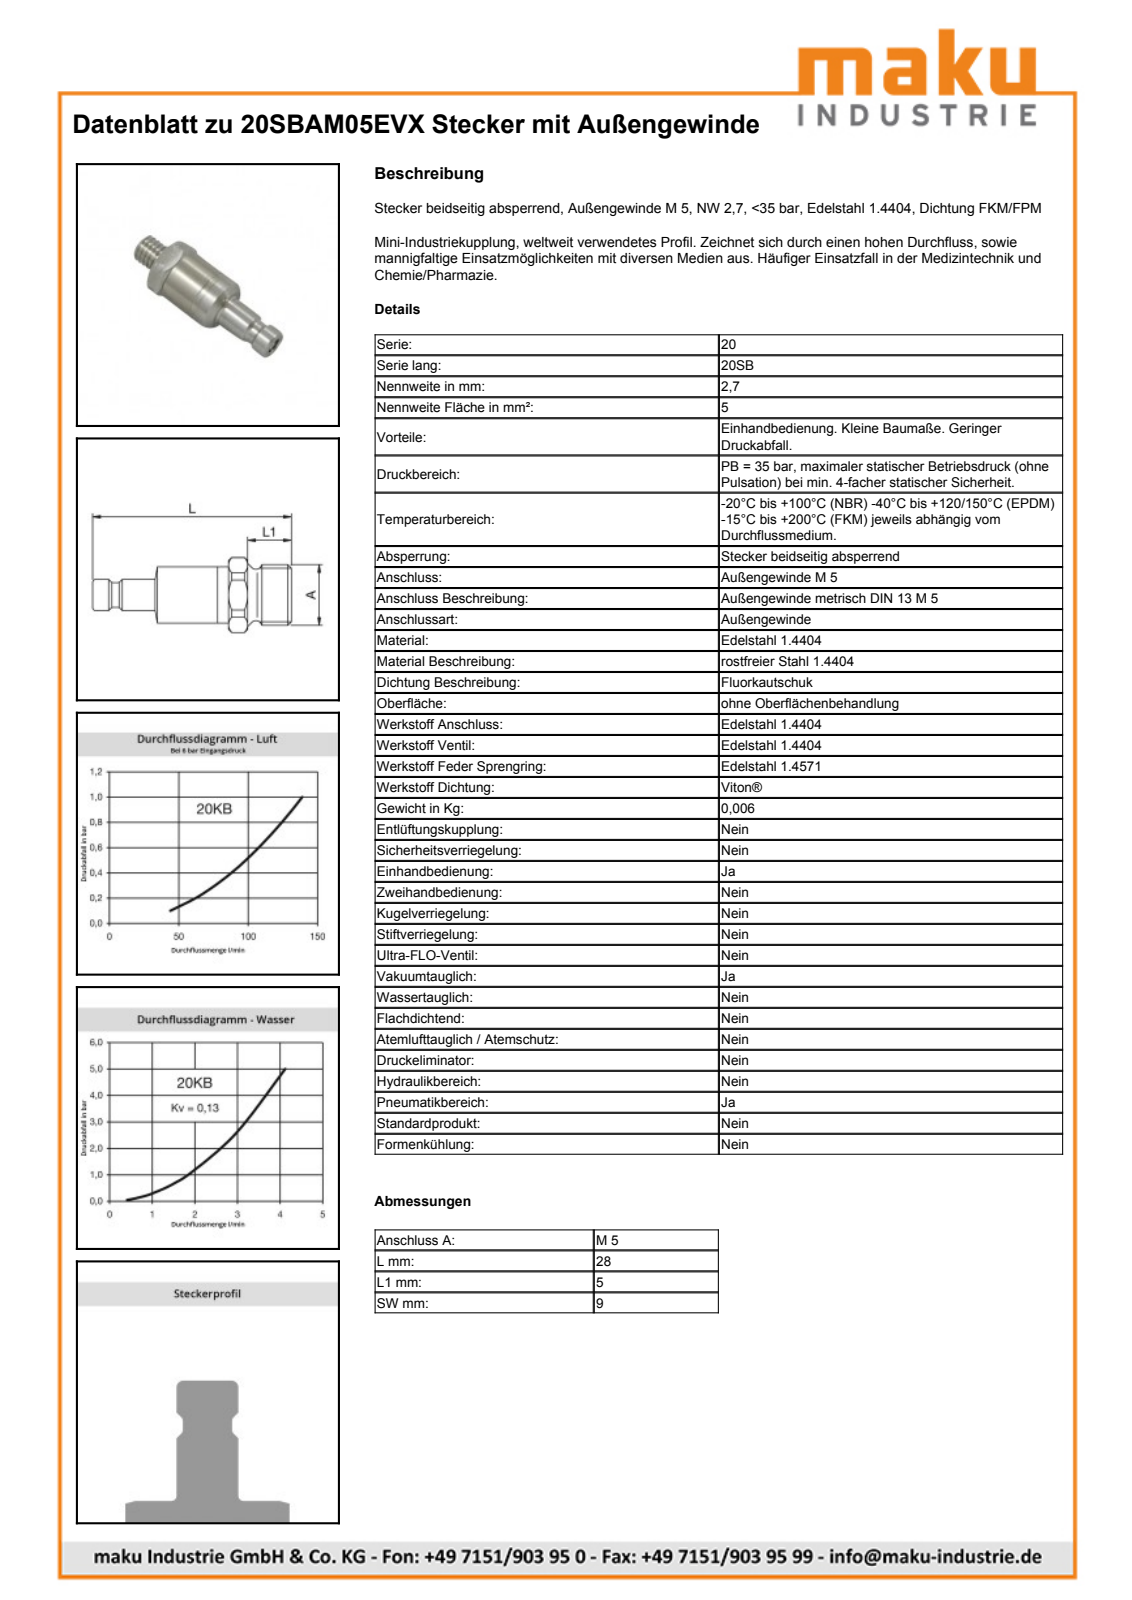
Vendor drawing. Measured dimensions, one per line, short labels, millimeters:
name: D109649
written by: Autodesk Inventor 2013 (AUTOMOTIVE_DESIGN)
unit: mm
bodies: 1 solid, 59 faces (13 planar, 17 cylindrical, 29 other)
size: 28.05 × 9.9 × 9.18
volume: 1 085 mm³; area: 971 mm²
holes: 1× ⌀6.3, 1× ⌀7.46, 1× ⌀8.1
bosses: 1× ⌀9, 1× ⌀7.3, 1× ⌀6.8, 1× ⌀6.2, 1× ⌀5, 1× ⌀3.95
rounds: 1× R4.95
face distances: 9, 10, 3.05, 13.05, 18.05, 8.05, 5, 20, 23.05, 28.05
